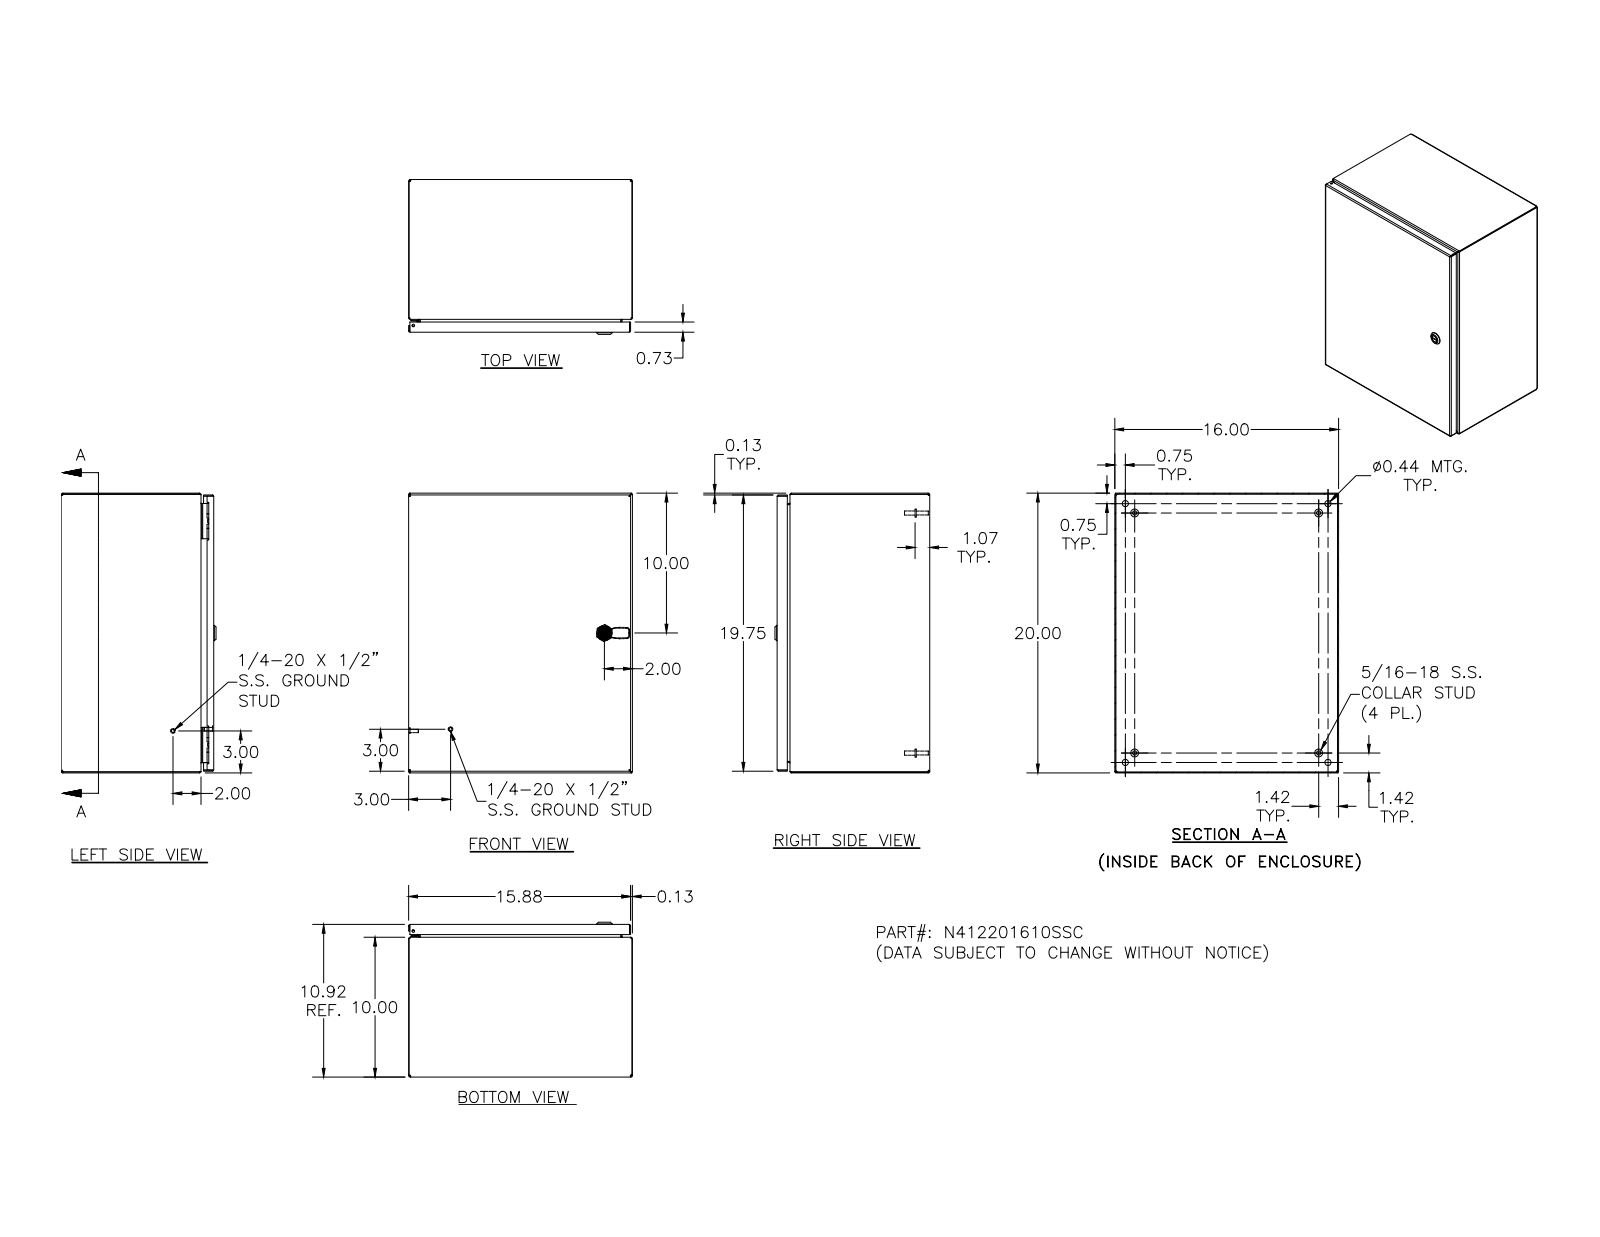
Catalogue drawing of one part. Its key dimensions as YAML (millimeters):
part_name: "N412201610SSC; N412201610SSCBKP; 388151; N4122016SSCLID (+8 more)"
step_written_by: "Autodesk Inventor 2011 (AUTOMOTIVE_DESIGN)"
units: millimeters
bodies: {solids: 34, faces: 1384, planar: 531, cylindrical: 509, other: 344}
overall_size: [508, 406.4, 281.3]
volume: 1829000
surface_area: 1958000
round_holes:
  - {diameter: 4.8, count: 5}
  - {diameter: 2.4, count: 4}
  - {diameter: 3.9, count: 4}
  - {diameter: 4.2, count: 4}
  - {diameter: 4.4, count: 4}
  - {diameter: 11.1, count: 4}
  - {diameter: 4, count: 2}
  - {diameter: 4.7, count: 1}
  - {diameter: 5, count: 1}
  - {diameter: 8, count: 1}
  - {diameter: 10, count: 1}
  - {diameter: 10.2, count: 1}
round_bosses_or_shafts:
  - {diameter: 6.4, count: 10}
  - {diameter: 14.3, count: 4}
  - {diameter: 9.1, count: 4}
  - {diameter: 8.1, count: 4}
  - {diameter: 7.6, count: 4}
  - {diameter: 7, count: 4}
  - {diameter: 6.5, count: 4}
  - {diameter: 4.2, count: 4}
partial_cylinders:
  - {radius: 0.8, count: 30}
  - {radius: 1.3, count: 26}
  - {radius: 2.7, count: 20}
  - {radius: 0.4, count: 18}
  - {radius: 3.2, count: 14}
  - {radius: 0.5, count: 9}
  - {radius: 0.8, count: 8}
  - {radius: 1.8, count: 8}
face_to_face_distances: [1.9, 275.4, 404.5, 506.1, 273.5, 277.3, 406.4, 402.6, 504.2, 508]
hole_center_spacings: [406.4, 0.4, 16.8, 406.6, 0.5, 12.7, 16.5, 16.6]
